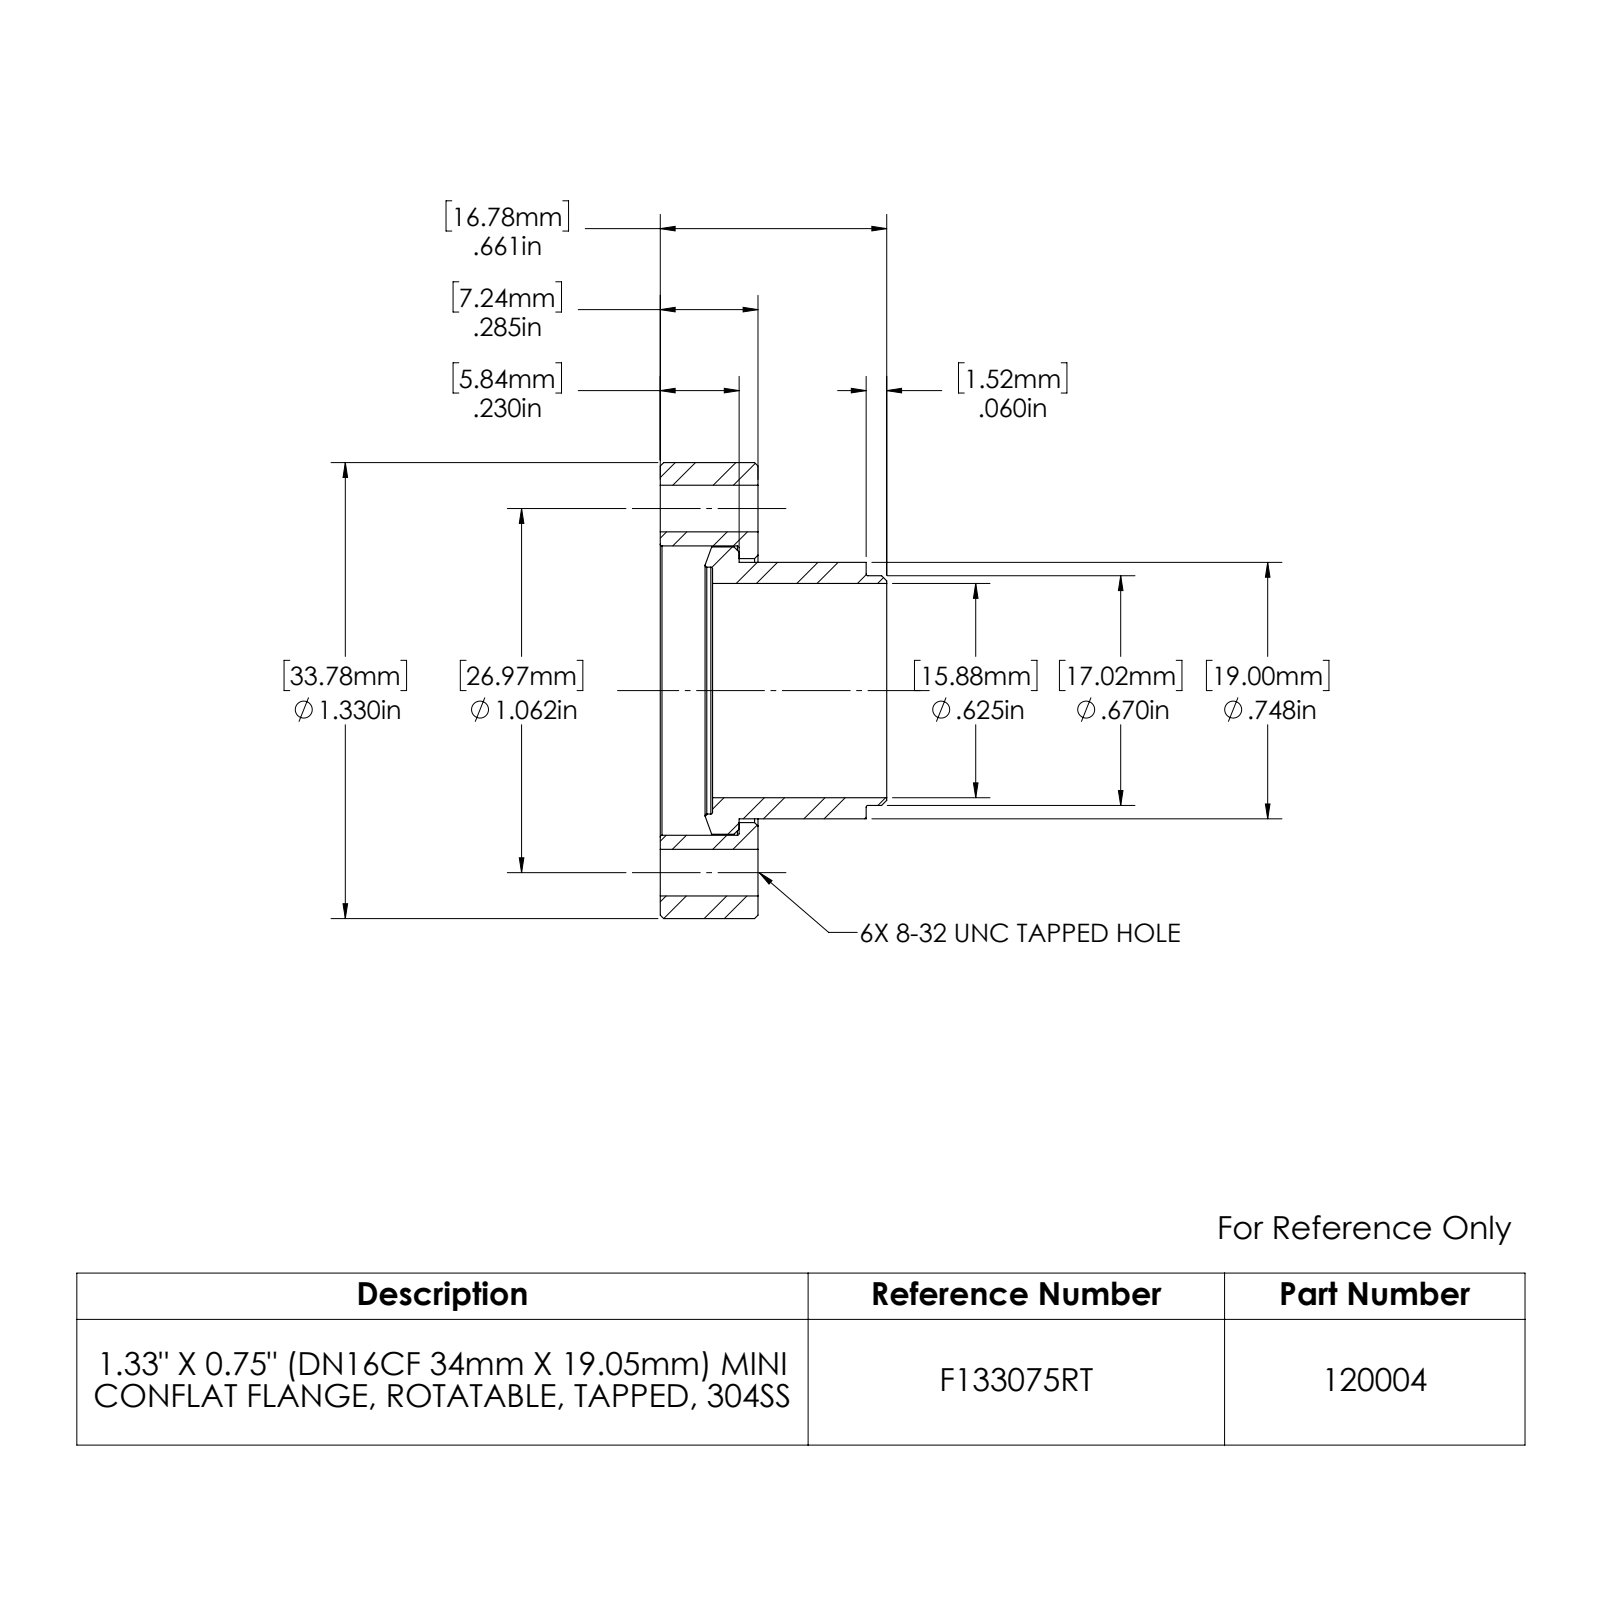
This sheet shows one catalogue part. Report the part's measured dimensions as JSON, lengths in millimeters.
{"part_name": "120004_A; 920000; 910004", "step_written_by": "SolidWorks 2022 (CONFIG_CONTROL_DESIGN)", "units": "millimeters", "bodies": {"solids": 2, "faces": 57, "planar": 7, "cylindrical": 28, "other": 22}, "overall_size": [33.8, 33.8, 16.8], "volume_mm3": 4720, "surface_area_mm2": 4490, "round_holes": [[3.5, 6], [15.9, 1], [18.3, 1], [19.6, 1], [21.4, 1]], "round_bosses_or_shafts": [[33.8, 1], [21.3, 1], [19, 1], [17, 1]], "face_to_face_distances": [7.2, 5.8, 1.4, 3.9, 2, 3.4, 15.2, 11.4, 9.4, 8], "hole_center_spacings": [13.5, 23.4, 13.5, 27, 27]}
